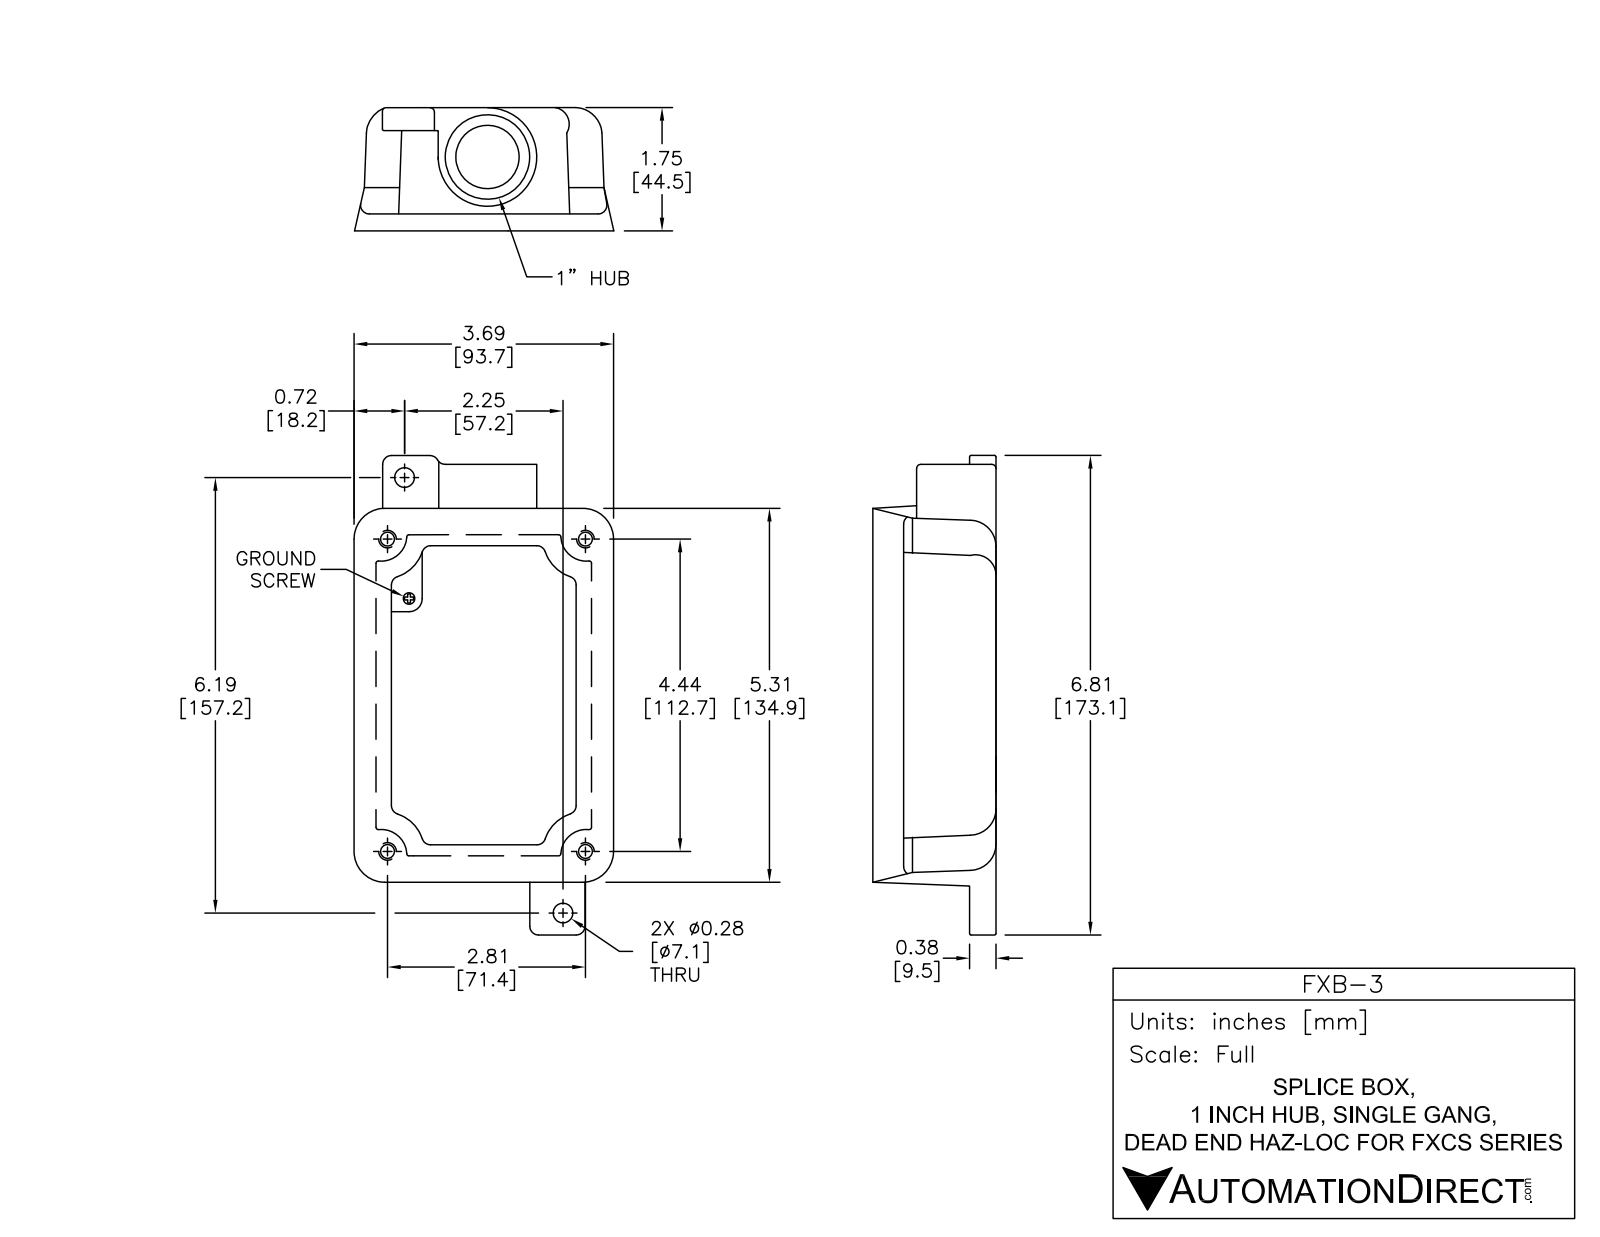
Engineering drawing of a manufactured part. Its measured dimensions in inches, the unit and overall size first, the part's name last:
Units: inches
Overall size (bounding box): 6.806 × 3.744 × 1.8
Round holes (diameter × count): ⌀0.266 ×4, ⌀0.32 ×2, ⌀0.8 ×1, ⌀0.945 ×1
Round bosses / shafts (diameter × count): ⌀0.325 ×1
Partial cylindrical surfaces — rounded edges, fillets, slot ends (radius × count): R0.02 ×27, R0.1 ×18, R0.15 ×11, R0.01 ×8, R0.26 ×4, R0.633 ×4, R0.08 ×2, R0.36 ×2
Main face-to-face distances: 0.29, 2.9, 0.165, 1.635, 1.8, 2.61, 3.19, 0.27, 4.54, 4.27
Hole centre spacings: 0.819, 0.906, 2.711, 2.736, 2.812, 2.867, 4.44, 4.623
Volume: 12.94 in³ · Surface area: 97.55 in²
Bodies: 2 solids, 392 faces (108 planar, 108 cylindrical, 176 other)
Part name (STEP PRODUCT): FXB-3
STEP written by: SolidWorks 2015 (AUTOMOTIVE_DESIGN)
